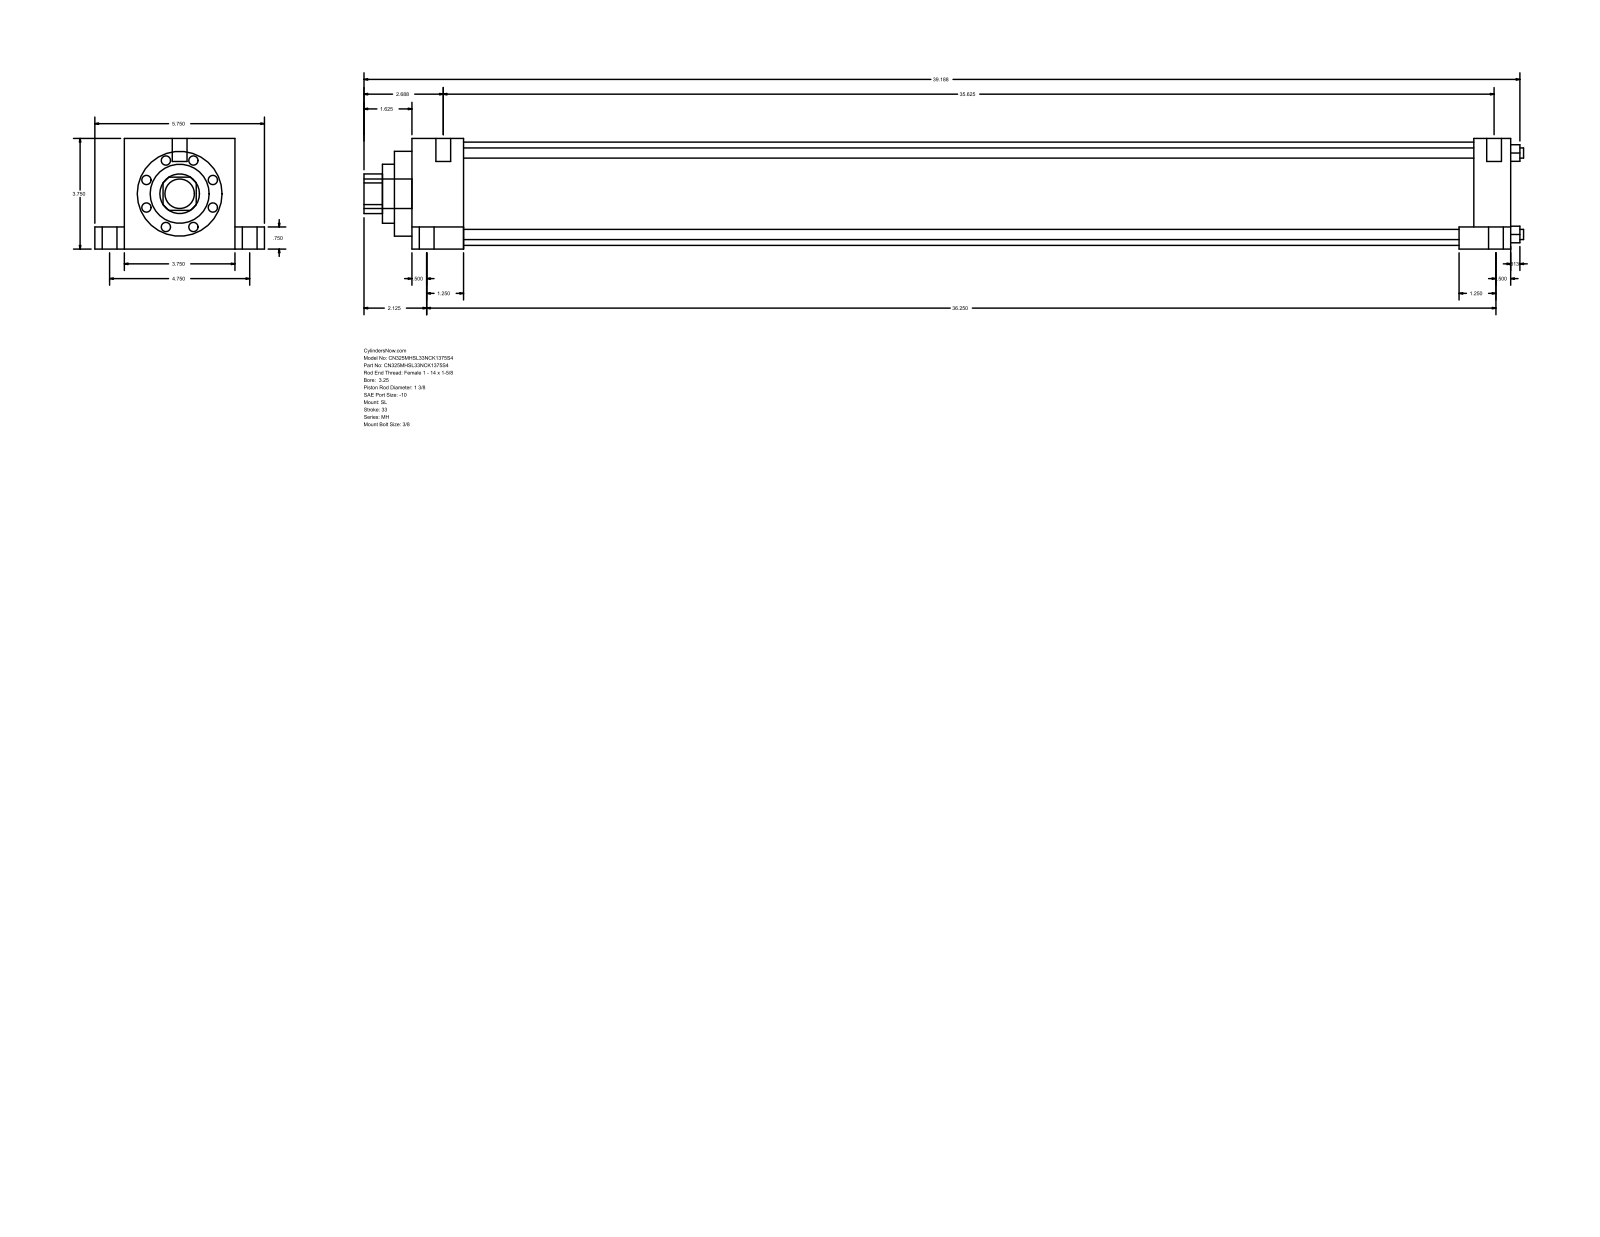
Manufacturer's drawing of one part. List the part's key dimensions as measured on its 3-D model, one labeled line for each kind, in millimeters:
Part name (STEP PRODUCT): MH_SL__0325_1.375
STEP written by: GSSL Pune (CONFIG_CONTROL_DESIGN)
Units: millimetres
Bodies: 0 solids, 110 faces (77 planar, 33 cylindrical, 0 other)
Overall size (bounding box): 998.54 × 146.05 × 95.25
Round holes (diameter × count): ⌀8.76 ×4, ⌀34.92 ×1, ⌀50.8 ×1, ⌀73.03 ×1, ⌀88.9 ×1
Round bosses / shafts (diameter × count): ⌀12.7 ×6, ⌀19.05 ×4, ⌀5.56 ×4, ⌀25.4 ×1
Partial cylindrical surfaces — rounded edges, fillets, slot ends (radius × count): R17.06 ×1
Main face-to-face distances: 95.24, 946.15, 44.45, 901.7, 25.41, 120.65, 19.05, 76.19, 914.4, 869.95
Hole centre spacings: 49.57, 70.1, 99.14
